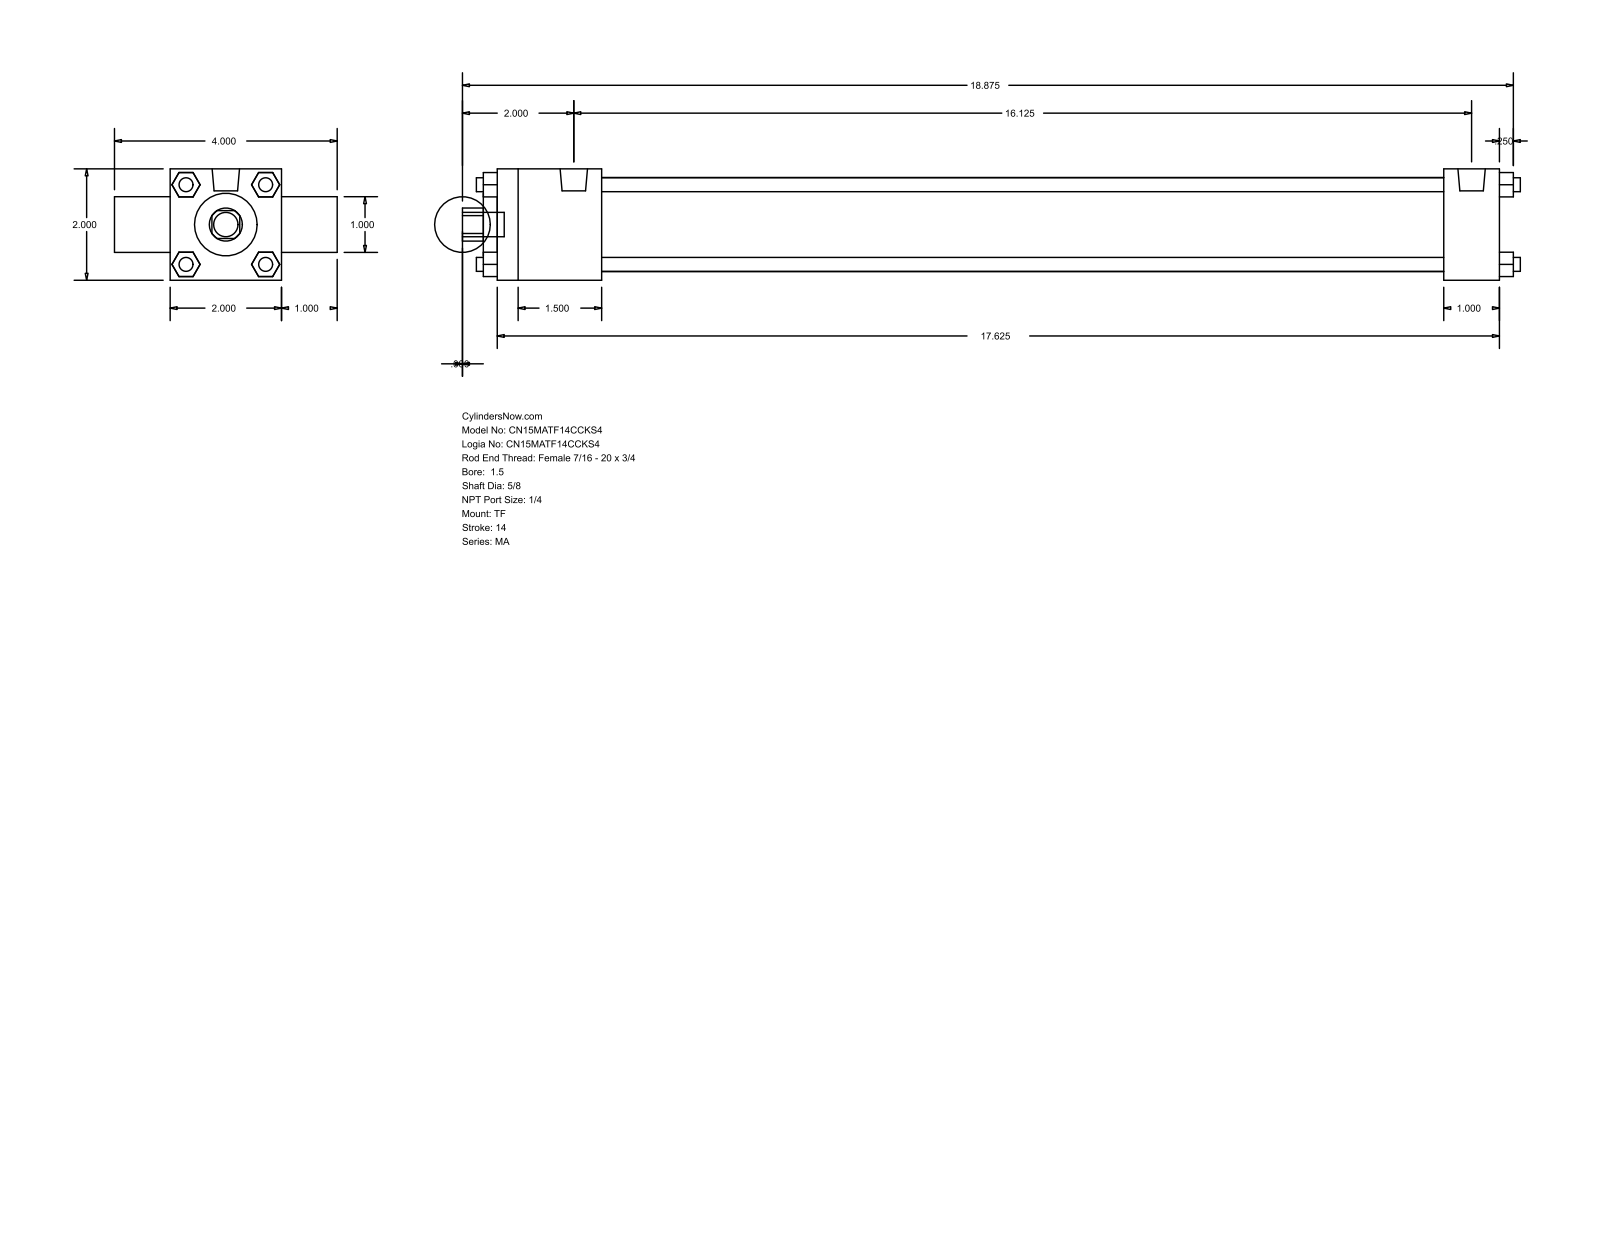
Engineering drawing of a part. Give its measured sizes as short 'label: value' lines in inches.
name: MA_TF__0150_0.625
written by: GSSL Pune (CONFIG_CONTROL_DESIGN)
unit: in
bodies: 0 solids, 120 faces (92 planar, 28 cylindrical, 0 other)
size: 19 × 4 × 2
holes: 1× ⌀0.625, 1× ⌀1, 1× ⌀1.125, 1× ⌀1.69
bosses: 4× ⌀0.25, 3× ⌀0.313, 2× ⌀0.492, 1× ⌀0.437
rounds: 1× R0.297
face distances: 2, 18, 1, 3, 1.875, 17, 15.125, 16.125, 1, 0.25
